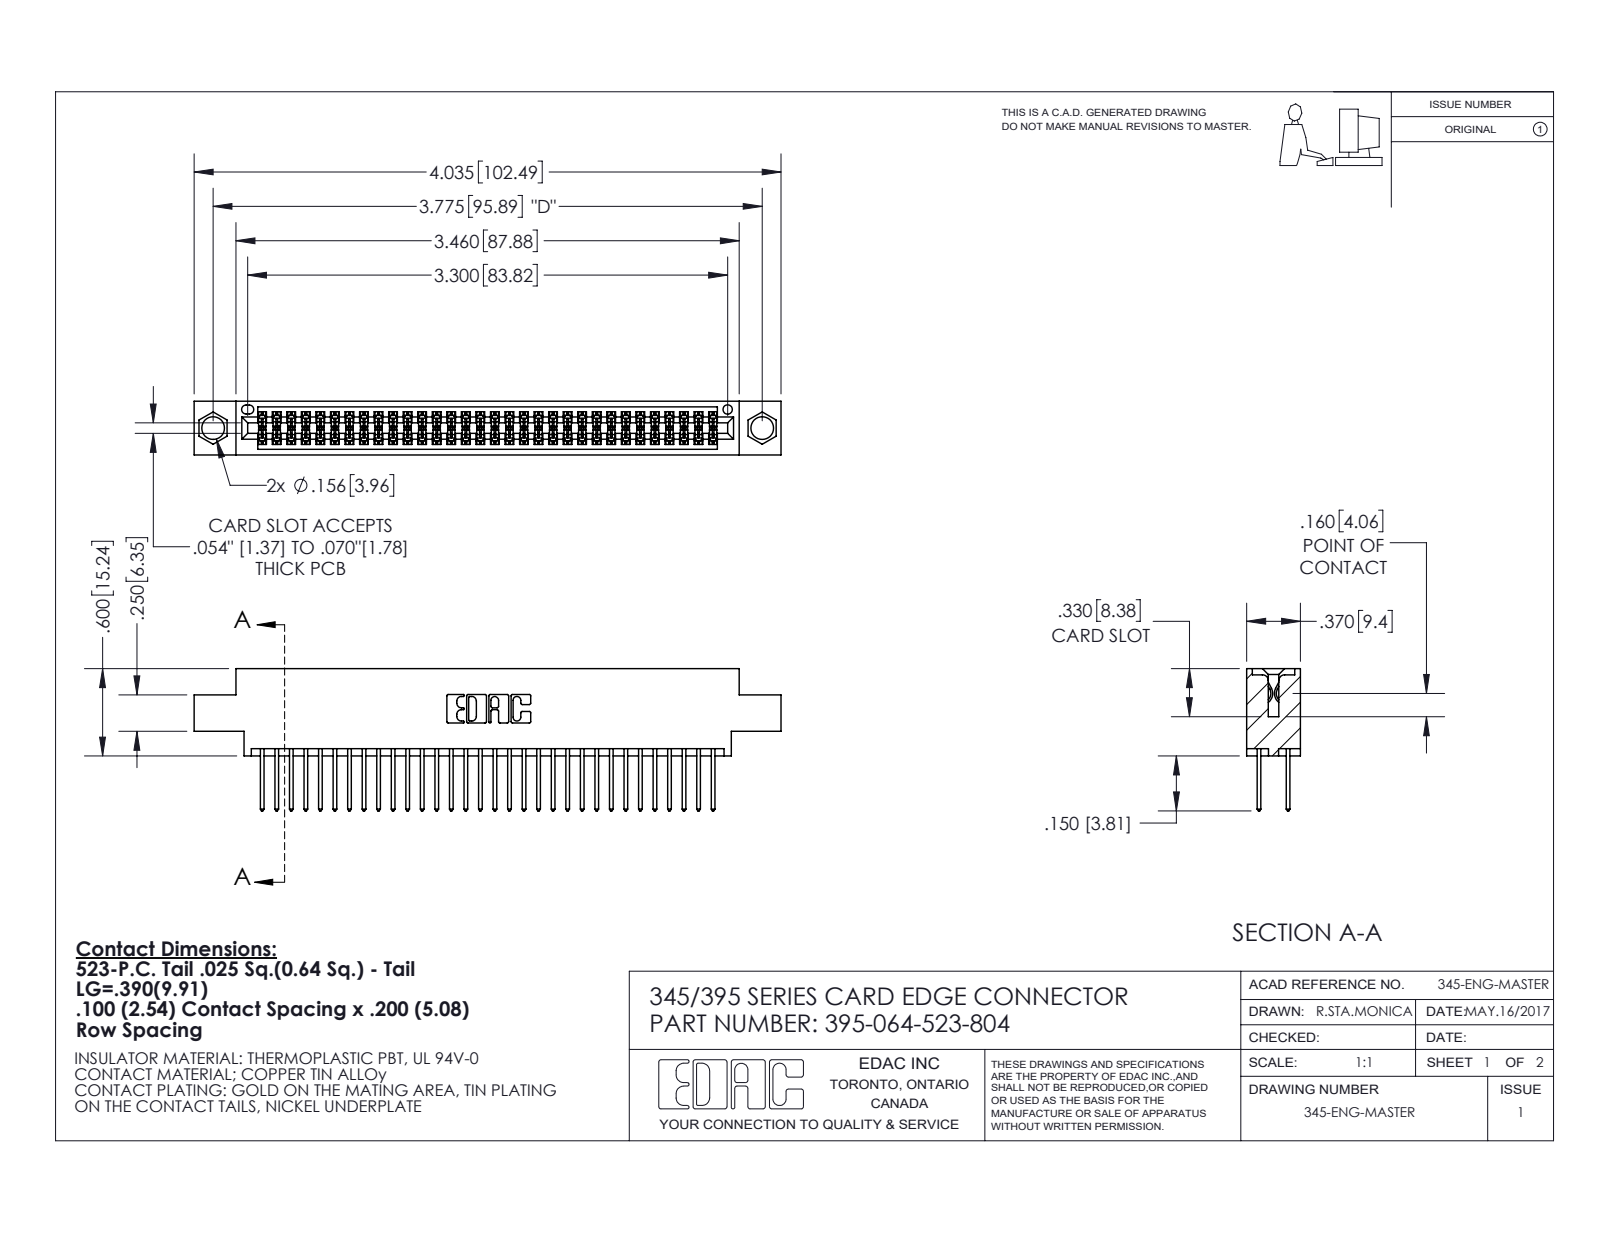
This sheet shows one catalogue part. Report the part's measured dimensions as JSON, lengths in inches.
{"part_name": "345 Part_0.170 Offset - 0.156 Dia-TI; 345-292-001_345-293-123; 395-064-523-804", "step_written_by": "SolidWorks 2020 (CONFIG_CONTROL_DESIGN)", "units": "inches", "bodies": {"solids": 65, "faces": 3344, "planar": 2210, "cylindrical": 1134, "other": 0}, "overall_size": [4.035, 0.977, 0.37], "volume_in3": 0.597, "surface_area_in2": 23, "round_holes": [[0.156, 2], [0.064, 1]], "partial_cylinders_radius": [[0.006, 128], [0.01, 64], [0.01, 22], [0.007, 6], [0.031, 6], [0.026, 3], [0.014, 2], [0.019, 2]], "face_to_face_distances": [0.072, 0.298, 0.2, 0.098, 0.272, 0.025, 0.37, 0.225, 0.175, 0.149], "hole_center_spacings": [0.27, 3.54, 3.775]}
